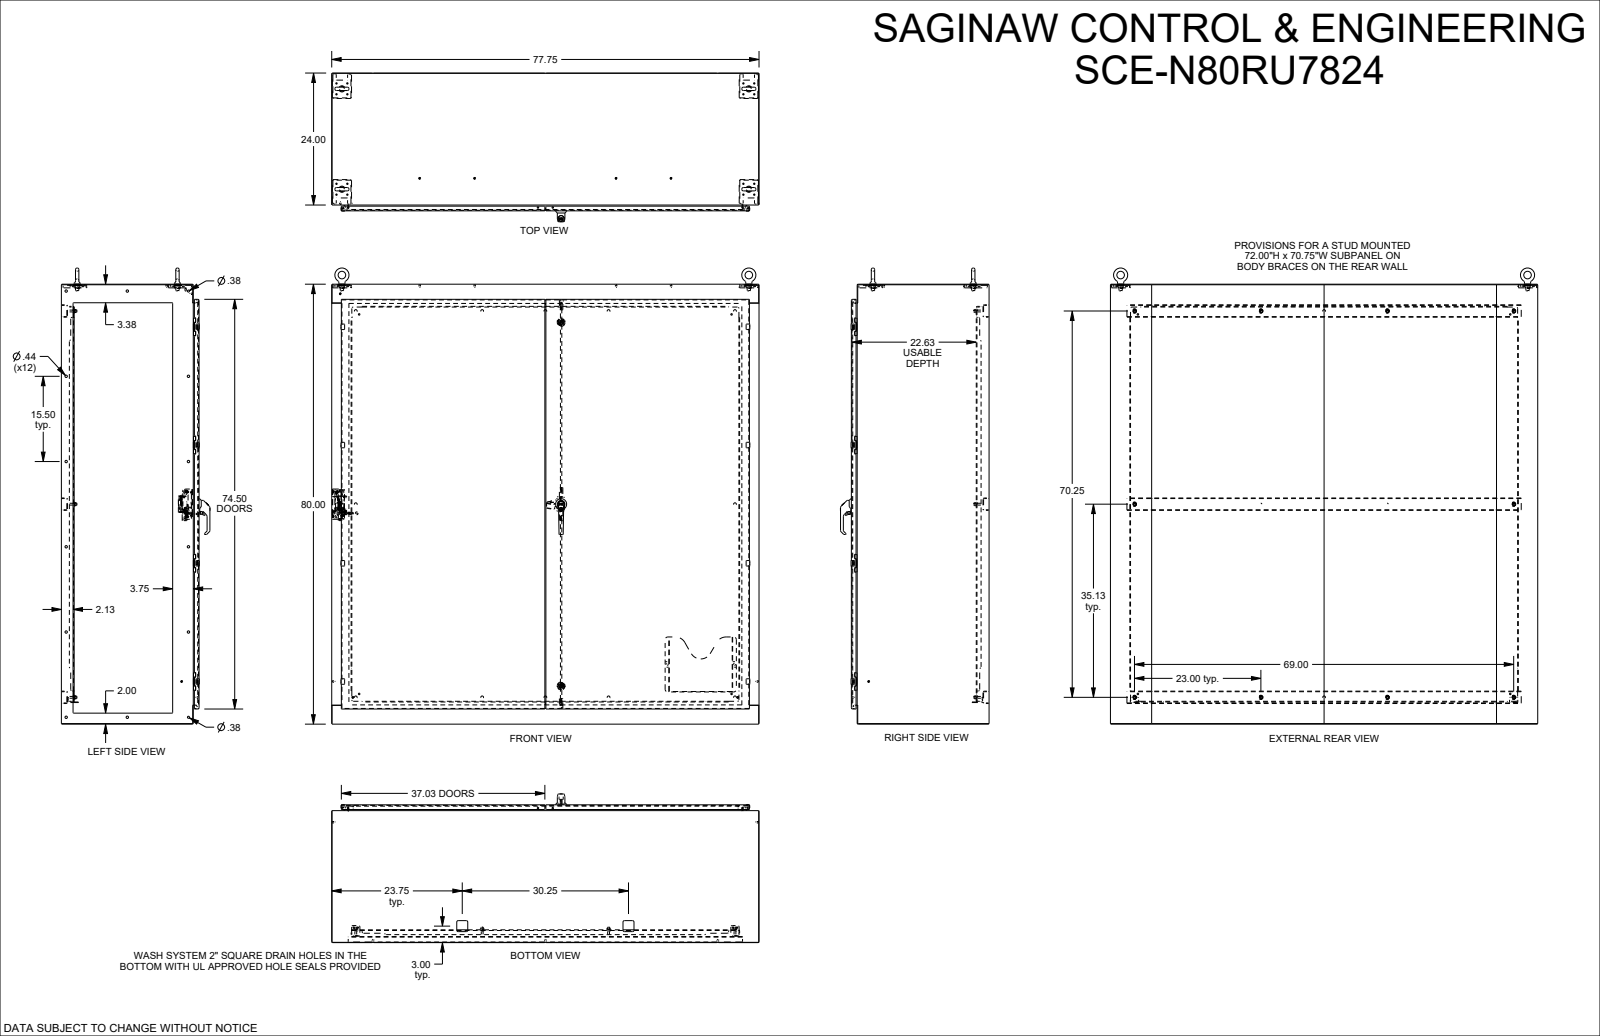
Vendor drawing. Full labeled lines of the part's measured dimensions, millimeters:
Part name (STEP PRODUCT): SCE-N80RU7824
STEP written by: SolidWorks 2023 (AUTOMOTIVE_DESIGN)
Units: millimetres
Bodies: 35 solids, 5049 faces (2384 planar, 1657 cylindrical, 1008 other)
Overall size (bounding box): 2106.8 × 1974.9 × 687
Volume: 35 920 000 mm³ · Surface area: 27 130 000 mm²
Round holes (diameter × count): ⌀6.4 ×19, ⌀9.5 ×18, ⌀5.2 ×16, ⌀6.2 ×16, ⌀11.1 ×12, ⌀1 ×8, ⌀5.5 ×8, ⌀4.3 ×4, ⌀6.5 ×4, ⌀5.2 ×2, ⌀8.7 ×2, ⌀9.1 ×2
Round bosses / shafts (diameter × count): ⌀4.3 ×24, ⌀6.4 ×16, ⌀6.1 ×16, ⌀5 ×10, ⌀29.8 ×4, ⌀15.2 ×4, ⌀35.6 ×2, ⌀10.3 ×2
Partial cylindrical surfaces — rounded edges, fillets, slot ends (radius × count): R0.8 ×102, R0.4 ×88, R3.2 ×67, R1 ×41, R4.2 ×38, R1.6 ×34, R1.6 ×34, R5.8 ×32
Main face-to-face distances: 2.6, 633.8, 631.2, 636.5, 2029.4, 607, 26.9, 2032, 2026.7, 1972.2
Hole centre spacings: 546.1, 50.3, 1092.2, 1850.8, 35.6, 1928.7, 393.7, 463.6
